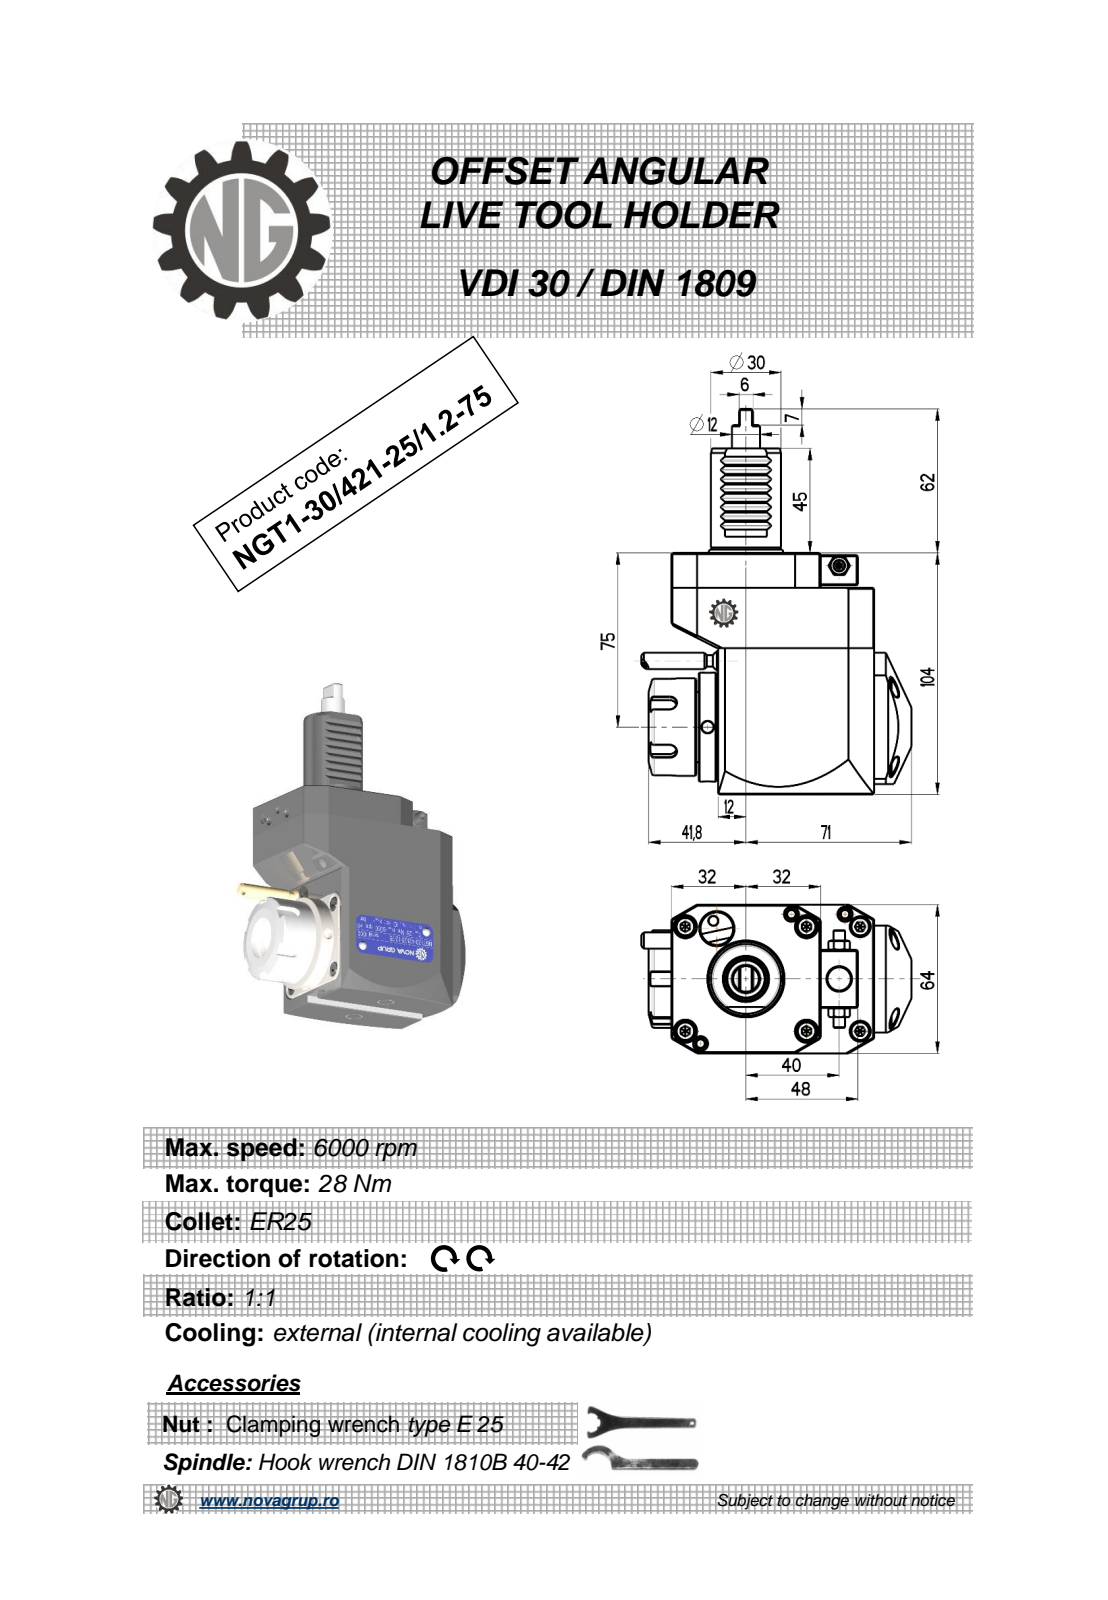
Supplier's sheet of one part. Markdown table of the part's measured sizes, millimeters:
| quantity | value |
| --- | --- |
| part name | NGT1_30_421_25_1_2_75 |
| STEP written by | PRO/ENGINEER BY PARAMETRIC TECHNOLOGY CORPORATION, 2010280 (CONFIG_CONTROL_DESIGN) |
| units | millimeters |
| bodies | 1 solid, 446 faces (204 planar, 96 cylindrical, 146 other) |
| overall size | 166 × 115.83 × 64 |
| volume | 559 182 mm³ |
| surface area | 53 342 mm² |
| round holes (diameter × count) | 5 × 2, 2.5 × 1, 3 × 1, 4.2 × 1, 9.5 × 1, 10 × 1, 20.3 × 1 |
| round bosses / shafts (diameter × count) | 8.96 × 2, 5 × 2, 47 × 1, 42 × 1, 36.4 × 1, 30 × 1, 12 × 1, 7 × 1 |
| partial cylindrical surfaces (radius × count) | 0.26 × 12, 0.3 × 8, 3 × 5, 3.5 × 4, 0.8 × 2, 160 × 2, 32 × 1 |
| main face-to-face distances | 64, 104, 87, 15, 89, 20, 19.8, 67.2, 0.5, 67 |
| hole center spacings | 33.19, 43, 56.45, 68, 89.54 |
